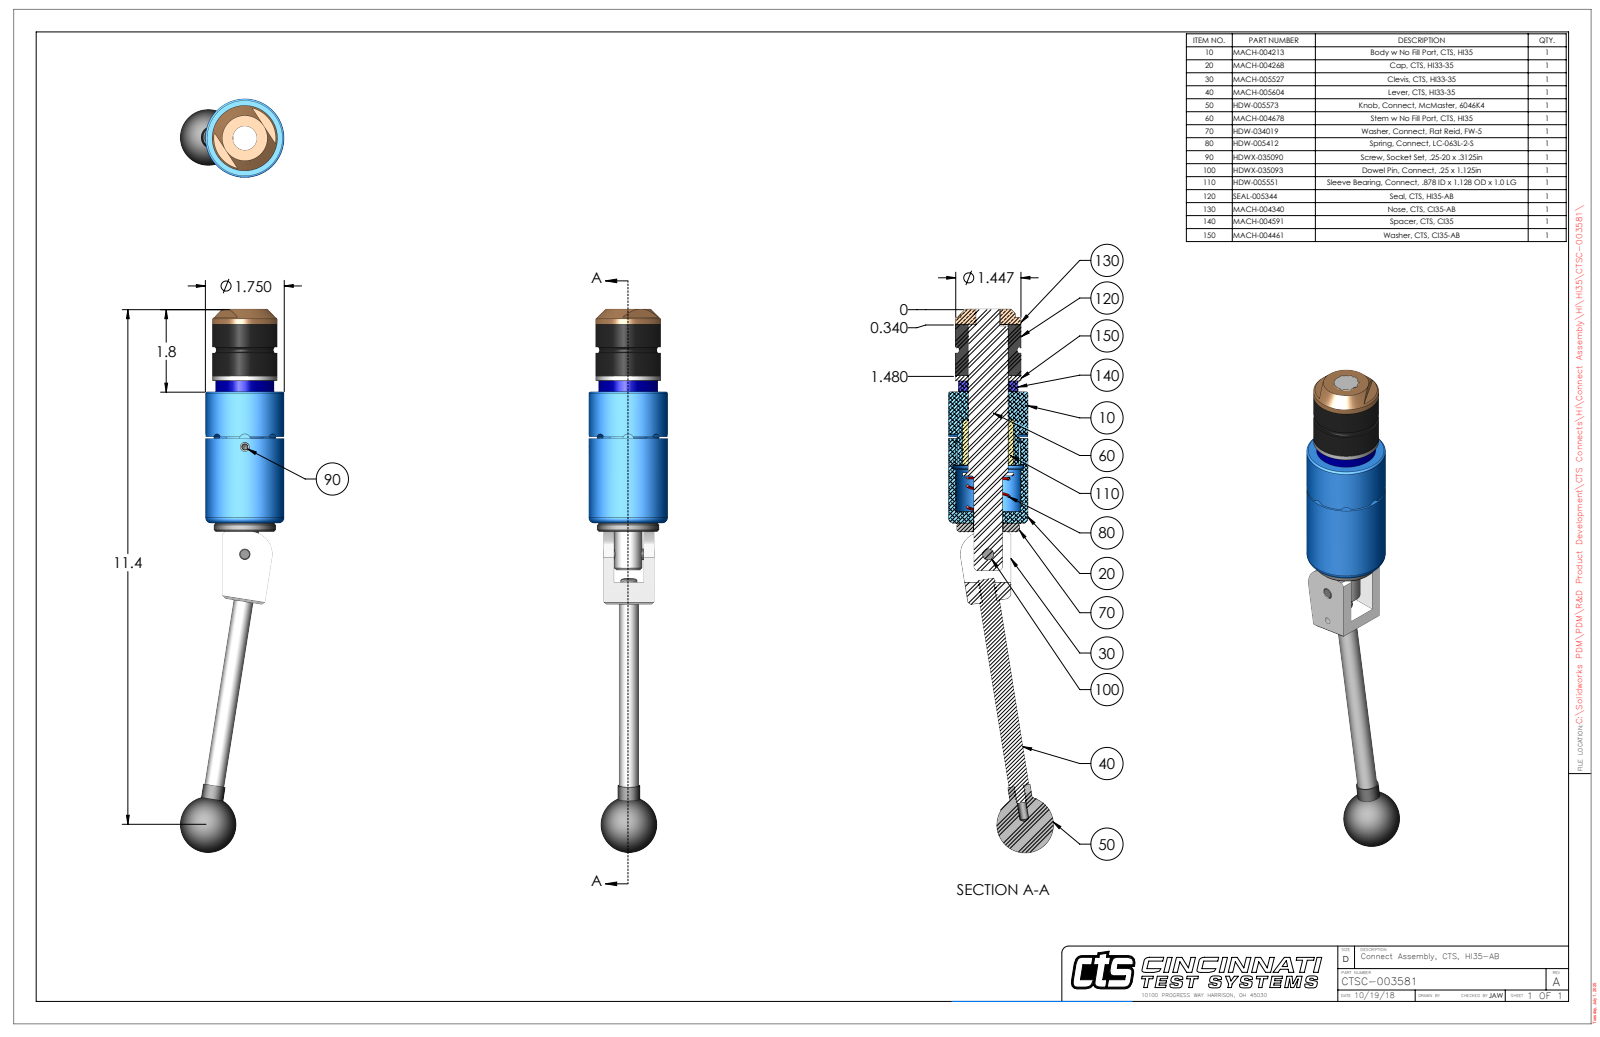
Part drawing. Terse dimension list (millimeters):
name: CTSC-003581
written by: SolidWorks 2023 (AUTOMOTIVE_DESIGN)
unit: mm
bodies: 11 solids, 260 faces (94 planar, 104 cylindrical, 62 other)
size: 305.8 × 58.7 × 44.5
volume: 212 900 mm³; area: 50 550 mm²
holes: 2× ⌀5.1, 1× ⌀3.8, 1× ⌀6.3, 1× ⌀6.4, 1× ⌀8, 1× ⌀13.5, 1× ⌀16.1, 1× ⌀16.7, 1× ⌀22.2, 1× ⌀22.3, 1× ⌀22.5, 1× ⌀36
bosses: 2× ⌀6.4, 1× ⌀44.5, 1× ⌀36.8, 1× ⌀35.1, 1× ⌀33.3, 1× ⌀22.1, 1× ⌀22.1, 1× ⌀15.9
rounds: 4× R3.2, 2× R0.7, 1× R12.7, 1× R17.7, 1× R21
face distances: 111.8, 37.8, 74, 29, 8.9, 82.9, 31.8, 2.8, 6.1, 80.1
hole spacings: 18.8, 60.4, 79.1
